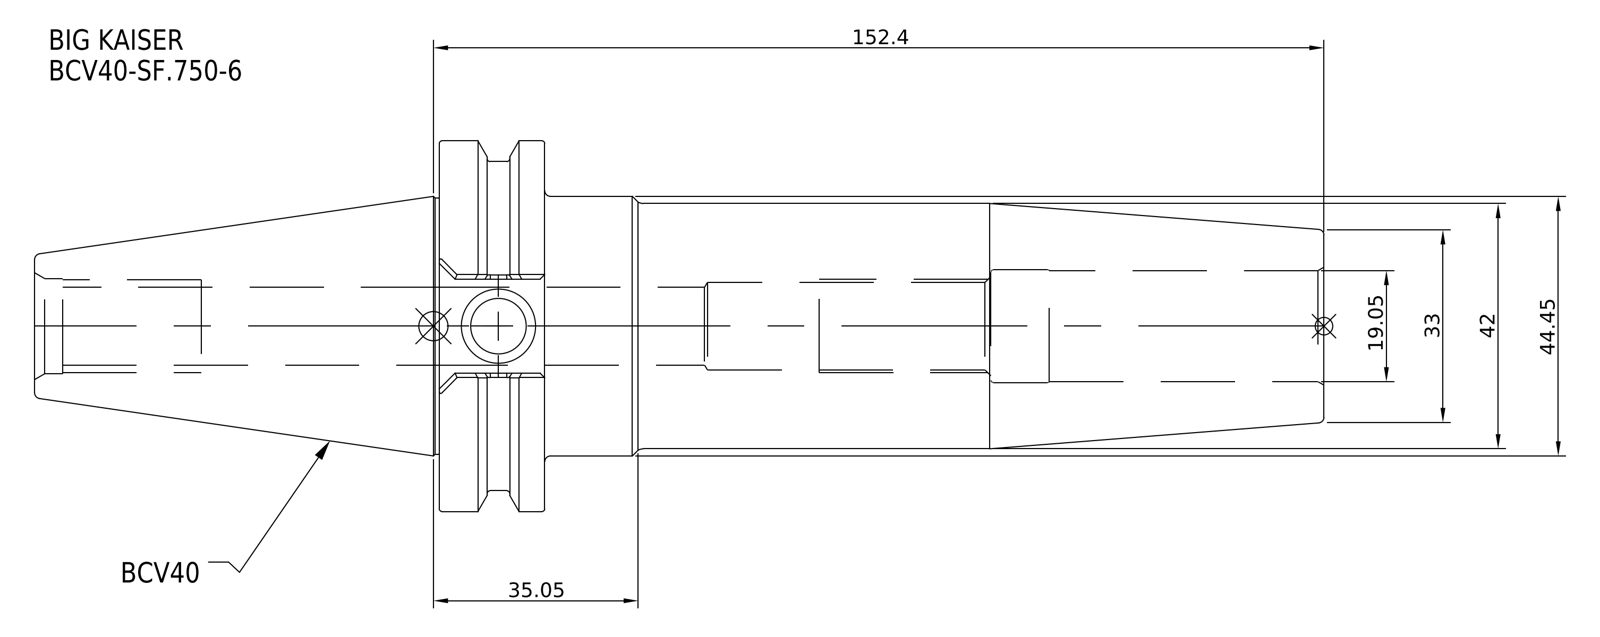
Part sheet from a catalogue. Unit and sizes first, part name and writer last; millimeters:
Units: millimetres
Overall size (bounding box): 220.65 × 63.5 × 63.5
Round holes (diameter × count): ⌀19.05 ×1
Round bosses / shafts (diameter × count): ⌀63.5 ×1, ⌀56.36 ×1, ⌀44.45 ×1, ⌀42 ×1
Main face-to-face distances: 18.05, 133.35, 151.4, 220.65, 87.3, 69.25, 47, 86.35, 104.4, 173.65
Volume: 279 080 mm³ · Surface area: 36 467 mm²
Bodies: 1 solid, 30 faces (8 planar, 14 cylindrical, 8 other)
Part name (STEP PRODUCT): BCV40-SF_750-6
STEP written by: SolidWorks 2021 (CONFIG_CONTROL_DESIGN)
